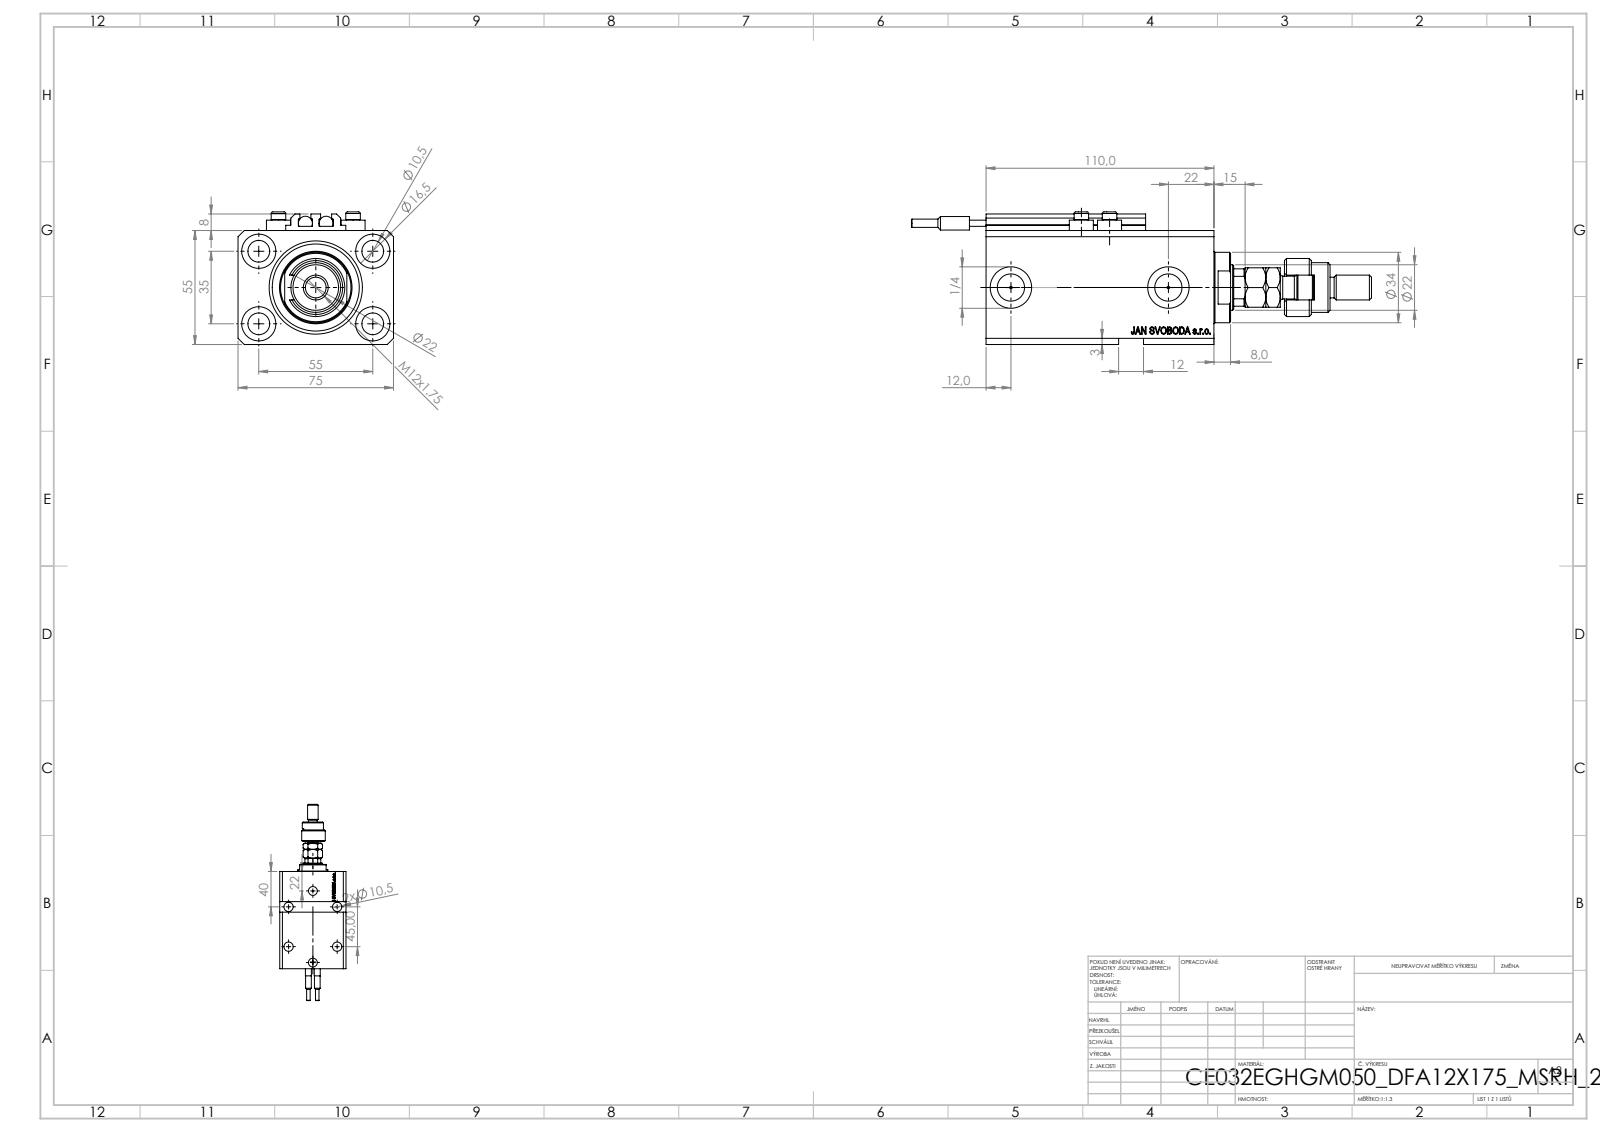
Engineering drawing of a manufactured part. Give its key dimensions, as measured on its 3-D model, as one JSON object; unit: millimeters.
{"part_name": "ALLEN BOLT V250CE; SWITCH_V250CE; MFA; V250CE_VC_E (+3 more)", "step_written_by": "SolidWorks 2019 (CONFIG_CONTROL_DESIGN)", "units": "millimeters", "bodies": {"solids": 12, "faces": 1221, "planar": 574, "cylindrical": 171, "other": 476}, "overall_size": [222, 75, 64], "volume_mm3": 402791, "surface_area_mm2": 105514, "round_holes": [[10.5, 9], [1.25, 4], [4, 4], [16.5, 4], [10, 2], [13.16, 2], [20, 2], [22, 1], [32, 1], [45, 1]], "round_bosses_or_shafts": [[11.6, 4], [7, 4], [6.8, 2], [6.5, 2], [4, 2], [34, 1], [28, 1], [24, 1]], "partial_cylinders_radius": [[0.2, 10], [9.75, 1], [10.5, 1]], "face_to_face_distances": [55, 75, 15, 3, 110, 57, 95, 9.9, 8, 19], "hole_center_spacings": [32.6, 32.87, 55, 68.74, 13.6, 14.09, 23.05, 25.81]}
